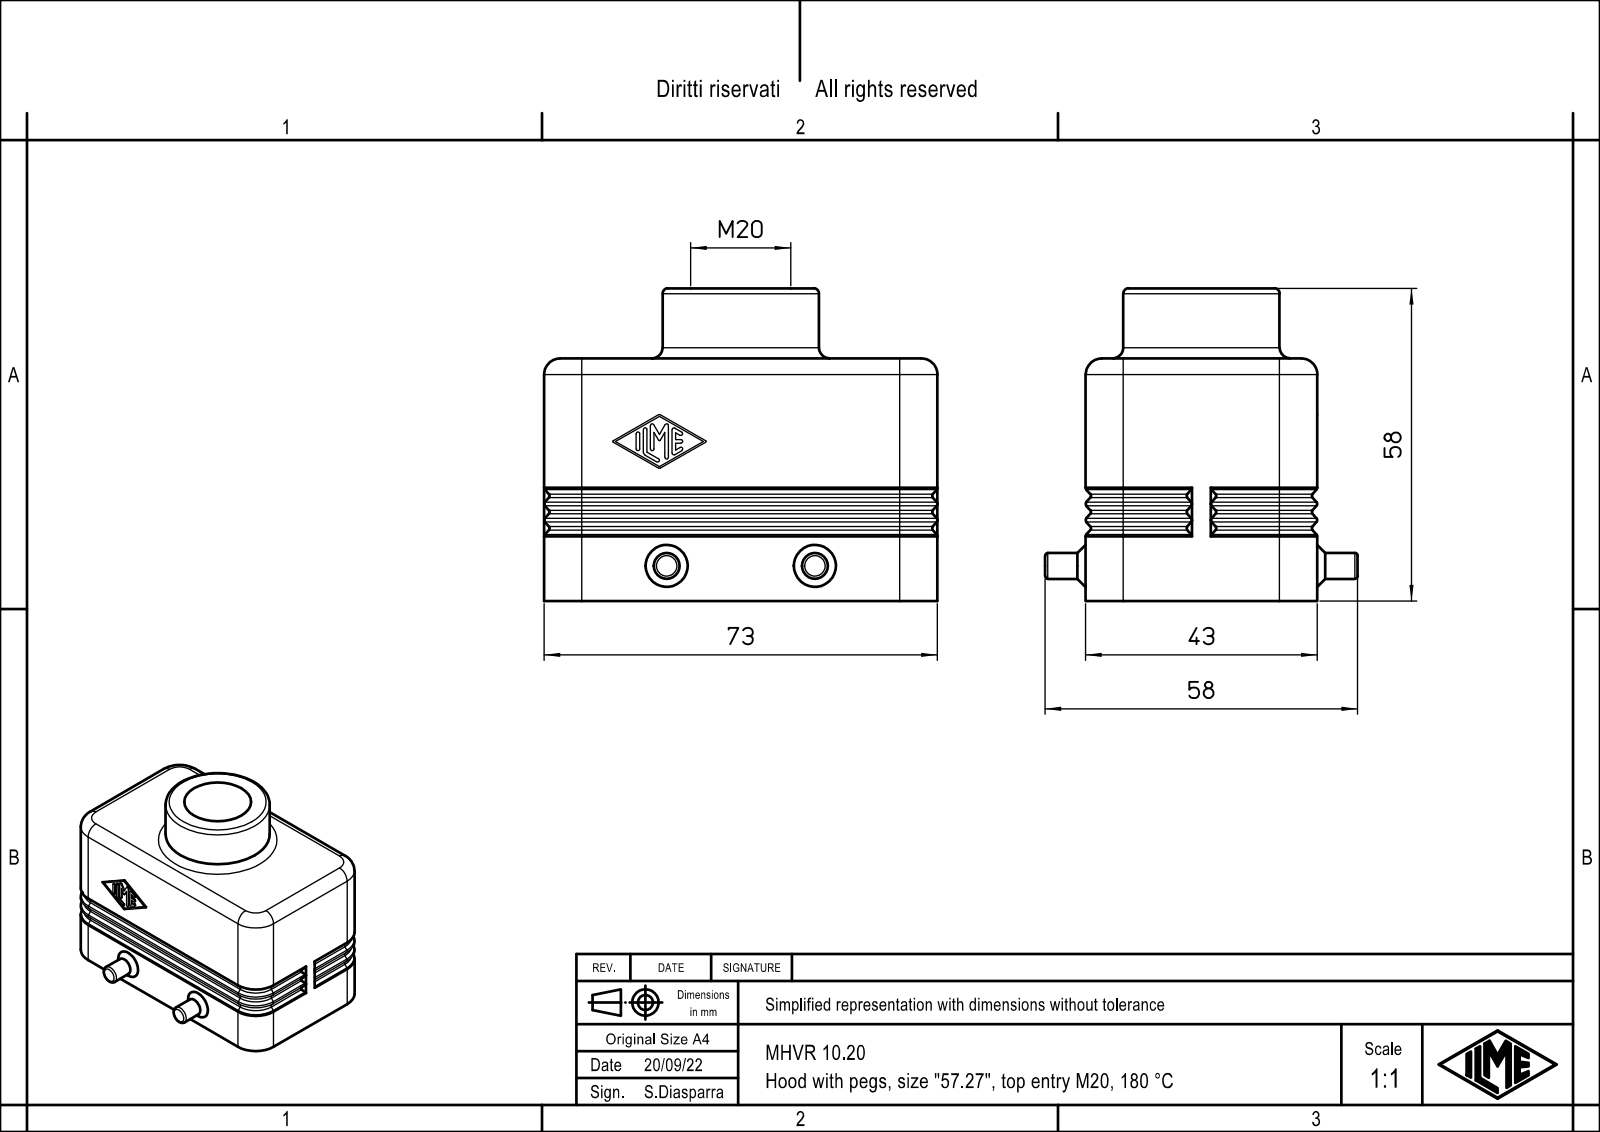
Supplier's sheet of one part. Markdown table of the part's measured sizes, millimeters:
| quantity | value |
| --- | --- |
| part name | MHVR 10.20 |
| STEP written by | Creo Elements/Direct Modeling 20.1B 02-Apr-2019 (C) Parametric Technology GmbH (AUTOMOTIVE_DESIGN) |
| units | millimeters |
| bodies | 1 solid, 389 faces (128 planar, 147 cylindrical, 114 other) |
| overall size | 73 × 58 × 58 |
| volume | 51 192 mm³ |
| surface area | 26 874 mm² |
| round holes (diameter × count) | 2.75 × 4, 16.5 × 1, 18.6 × 1 |
| round bosses / shafts (diameter × count) | 4.8 × 2, 29 × 1 |
| partial cylindrical surfaces (radius × count) | 0.5 × 44, 1.5 × 22, 0.33 × 15, 3 × 8, 3.5 × 4, 7 × 4, 0.17 × 2, 0.17 × 1 |
| main face-to-face distances | 3.5, 39.5, 36, 43, 2.8, 69.5, 73, 2, 42.2, 45 |
| hole center spacings | 31.54, 27, 57, 63.07 |
